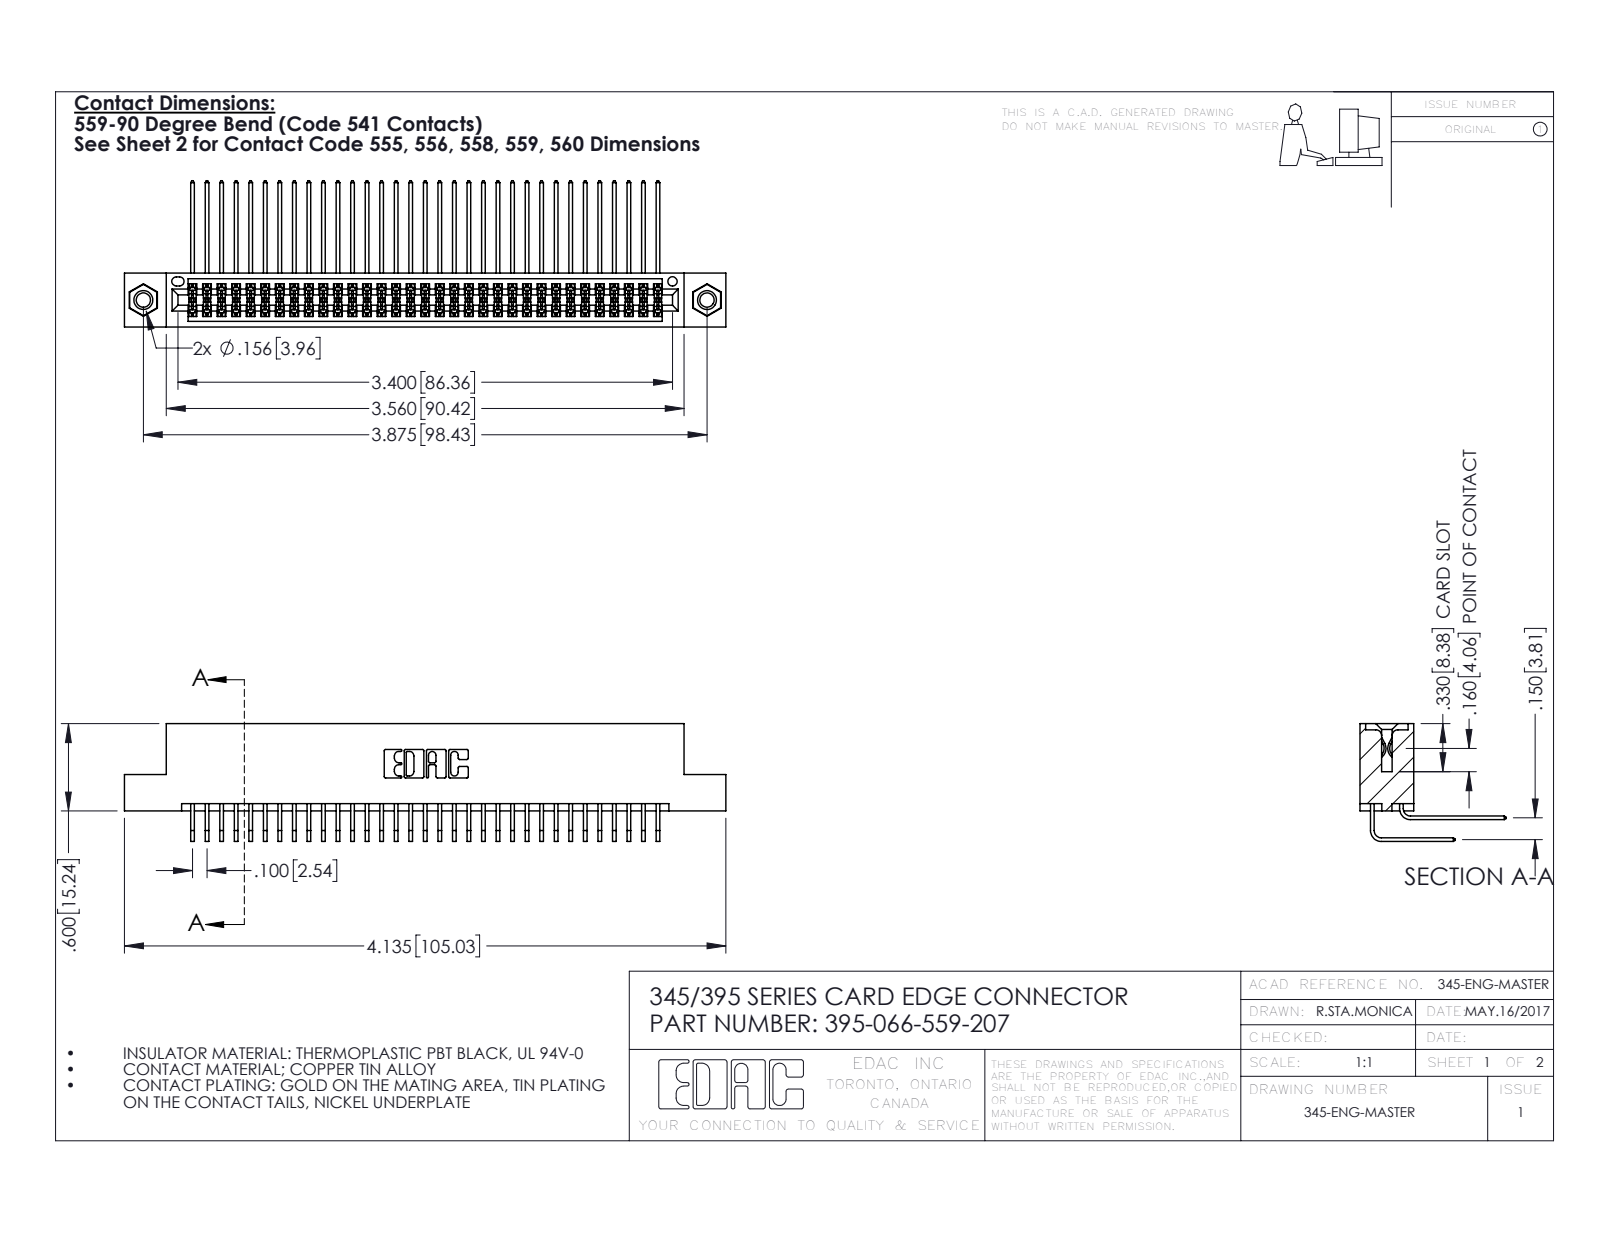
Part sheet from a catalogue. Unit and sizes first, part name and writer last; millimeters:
Units: millimetres
Overall size (bounding box): 105 × 25.5 × 20.5
Round holes (diameter × count): ⌀2.5 ×2, ⌀3.2 ×2, ⌀4 ×2, ⌀1.6 ×1
Round bosses / shafts (diameter × count): ⌀3.9 ×2
Partial cylindrical surfaces — rounded edges, fillets, slot ends (radius × count): R0.2 ×100, R0.3 ×22, R0.2 ×6, R0.8 ×6, R0.7 ×3, R0.4 ×2, R0.5 ×2, R0.6 ×2
Main face-to-face distances: 1.8, 7.6, 5.1, 9.4, 2.5, 6.9, 0.6, 5.7, 4.4, 3.8
Hole centre spacings: 6.9, 92.5, 98.4
Volume: 10 500 mm³ · Surface area: 17 140 mm²
Bodies: 69 solids, 3618 faces (2422 planar, 1180 cylindrical, 16 other)
Part name (STEP PRODUCT): 345-292-001_559 Tail - 2; 345-292-001_558 559 Tail - 1; 345-250-001_345-250-005-103; 395-066-559-207 (+1 more)
STEP written by: SolidWorks 2016 (CONFIG_CONTROL_DESIGN)
